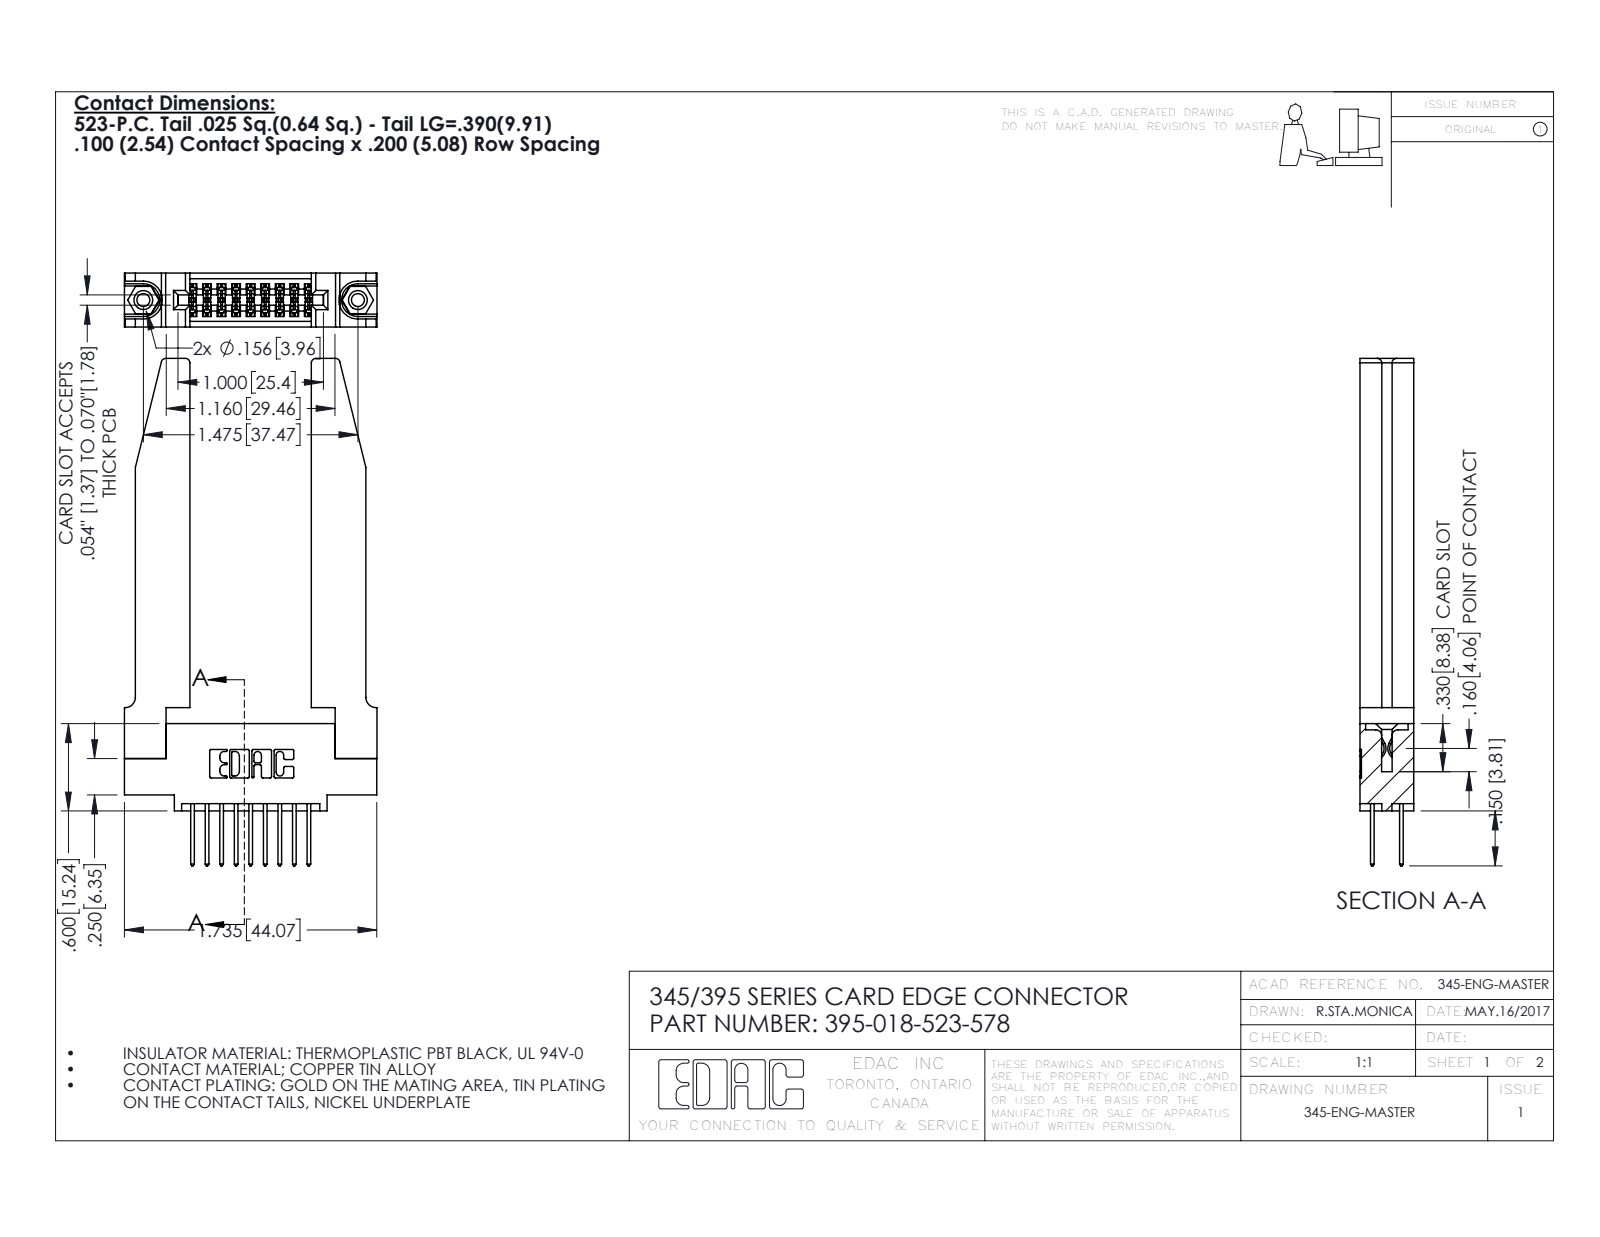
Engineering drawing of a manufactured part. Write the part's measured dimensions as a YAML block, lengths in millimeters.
part_name: "345-292-001_345-293-123; 345 Part_0.110 Offset - 0.156 Dia-TH; 345-250-001_345-250-001-102; 345-220-078_345-220-078 (+1 more)"
step_written_by: "SolidWorks 2016 (CONFIG_CONTROL_DESIGN)"
units: millimeters
bodies: {solids: 23, faces: 1264, planar: 820, cylindrical: 392, other: 52}
overall_size: [88.6, 44.1, 9.4]
volume: 11700
surface_area: 12280
round_holes:
  - {diameter: 2.3, count: 2}
  - {diameter: 3.2, count: 2}
  - {diameter: 4, count: 2}
  - {diameter: 1.6, count: 1}
round_bosses_or_shafts:
  - {diameter: 3.9, count: 2}
partial_cylinders:
  - {radius: 0.2, count: 27}
  - {radius: 0.3, count: 22}
  - {radius: 0.3, count: 18}
  - {radius: 0.8, count: 8}
  - {radius: 0.2, count: 6}
  - {radius: 0.8, count: 6}
  - {radius: 0.7, count: 3}
  - {radius: 0.4, count: 2}
face_to_face_distances: [9.4, 1.8, 7.6, 3.8, 3.8, 5.6, 2, 21.2, 2.5, 6.9]
hole_center_spacings: [6.9, 31.6, 37.5]
